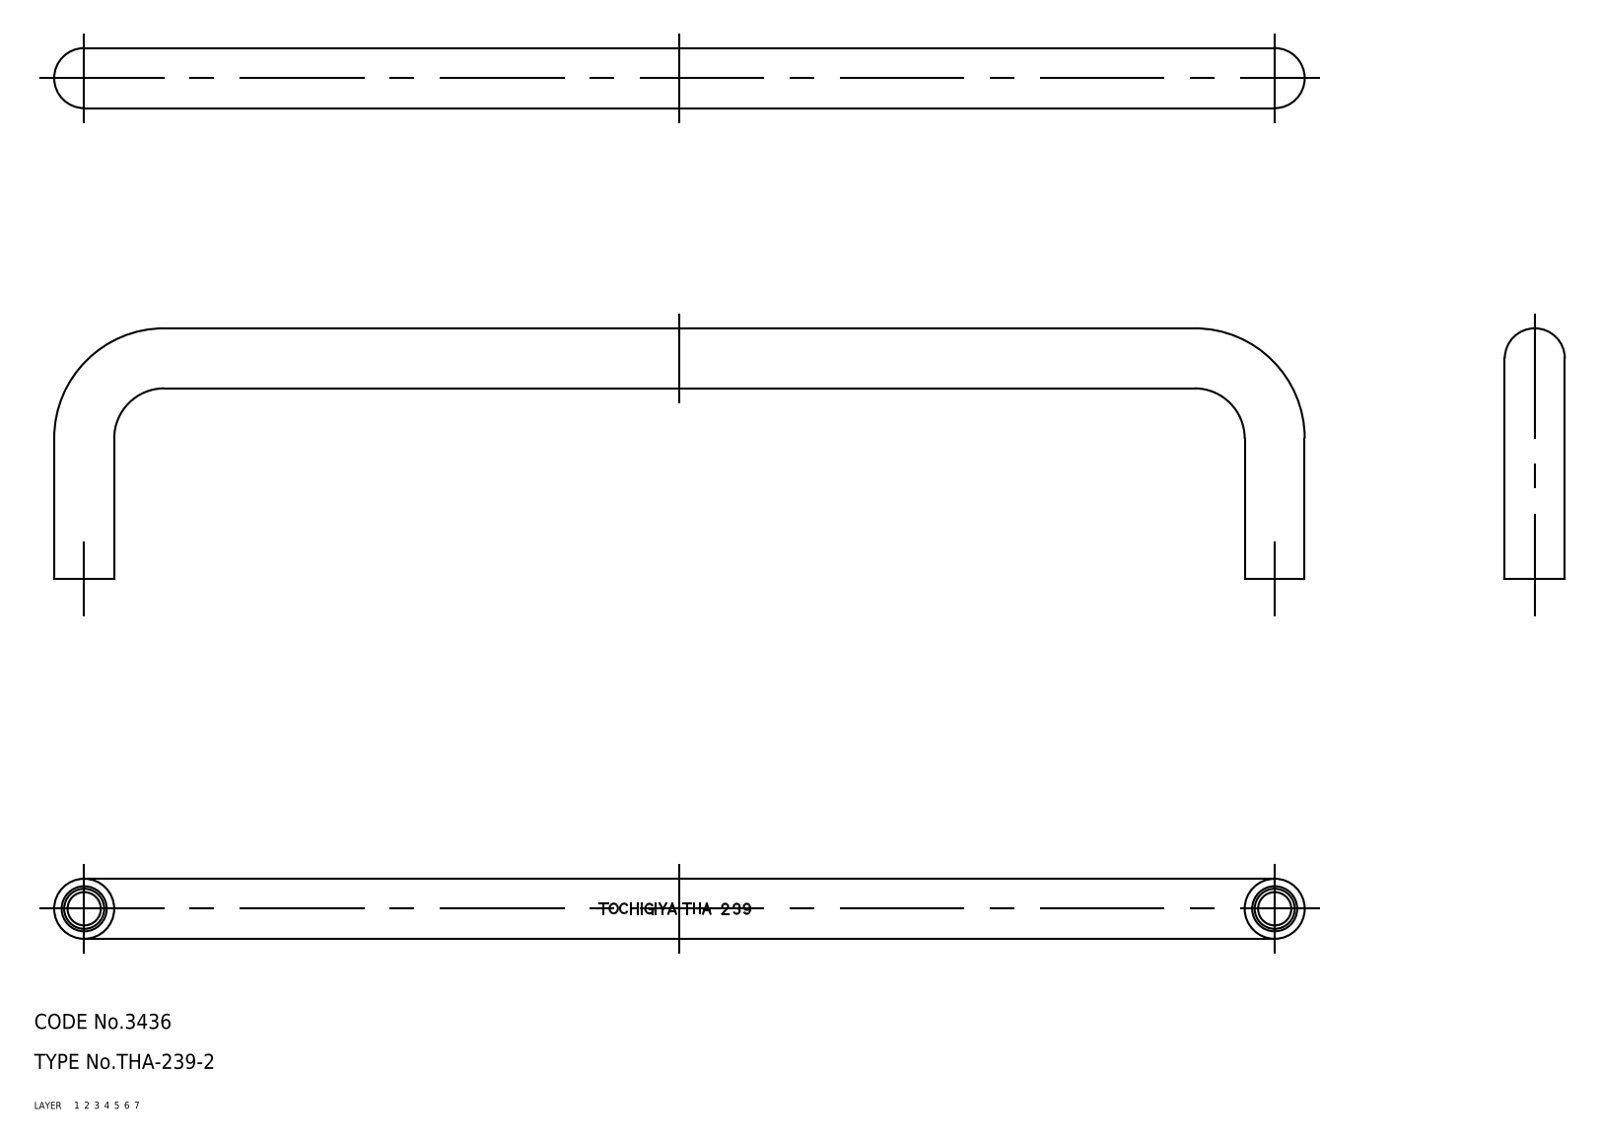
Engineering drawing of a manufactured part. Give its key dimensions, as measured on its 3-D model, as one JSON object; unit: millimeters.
{"part_name": "pull", "step_written_by": "CADfix (AUTOMOTIVE_DESIGN)", "units": "millimeters", "bodies": {"solids": 1, "faces": 18, "planar": 0, "cylindrical": 0, "other": 18}, "overall_size": [250, 50, 12], "volume_mm3": 34232, "surface_area_mm2": 12541}
